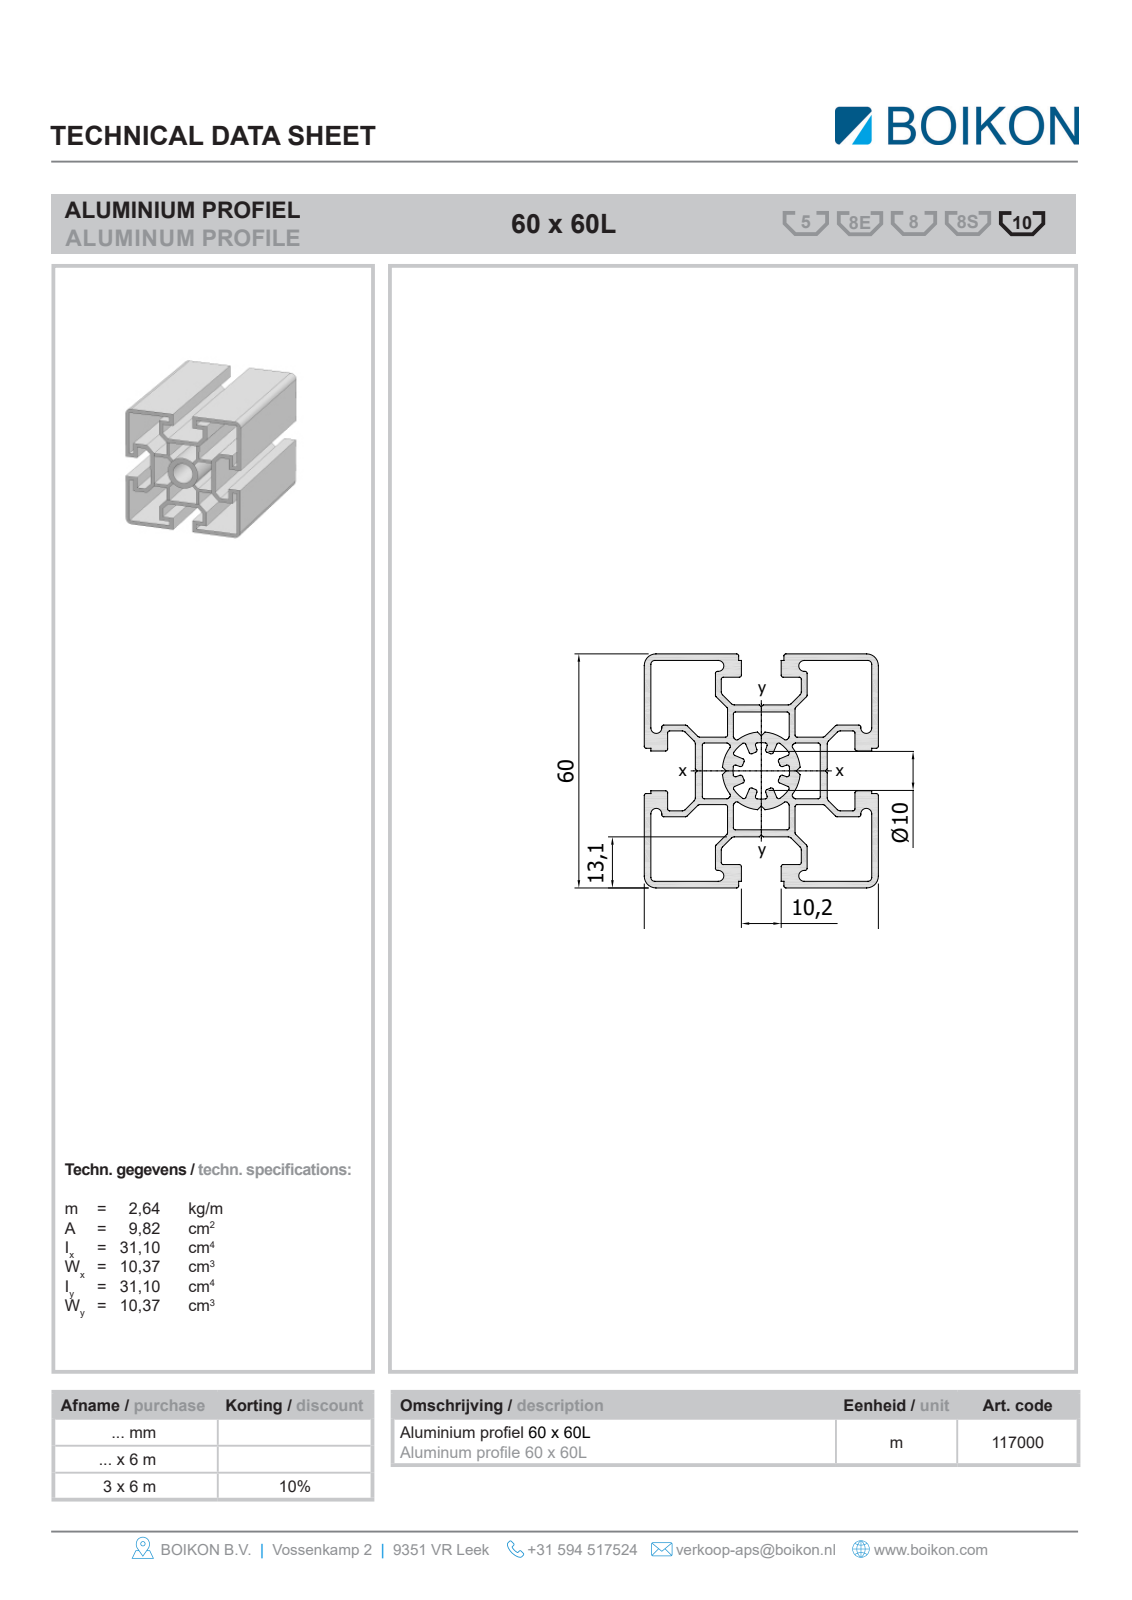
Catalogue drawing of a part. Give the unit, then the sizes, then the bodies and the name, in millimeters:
Units: millimetres
Overall size (bounding box): 1000 × 60 × 60
Round holes (diameter × count): ⌀10 ×1
Round bosses / shafts (diameter × count): ⌀20 ×1
Partial cylindrical surfaces — rounded edges, fillets, slot ends (radius × count): R1.4 ×8, R1 ×4, R3 ×4, R0.5 ×2
Main face-to-face distances: 1.69, 58.31, 1.5, 18.9, 60, 3.1, 12.25, 16.85, 56.62, 13.75
Volume: 1 058 000 mm³ · Surface area: 938 261 mm²
Bodies: 1 solid, 129 faces (106 planar, 23 cylindrical, 0 other)
Part name (STEP PRODUCT): Root; 11700060x60LBOIKON0
STEP written by: HiCAD 2013 1802.4 Build 509 (AUTOMOTIVE_DESIGN)
